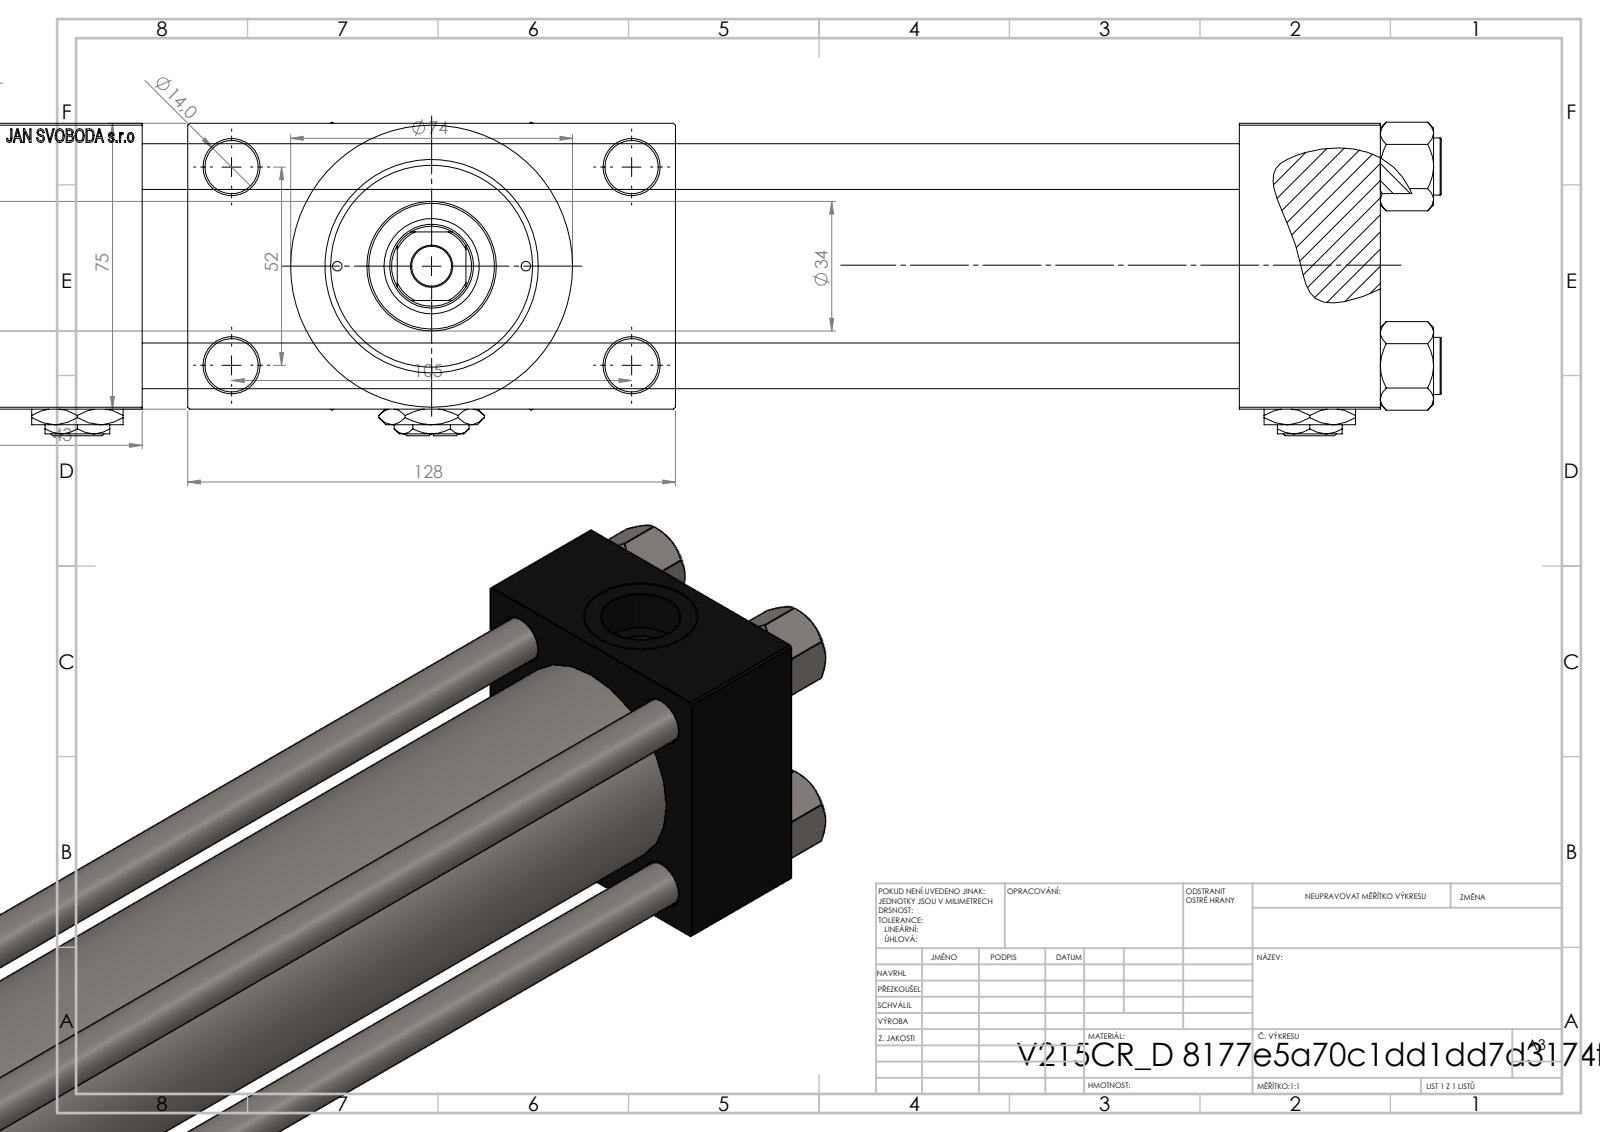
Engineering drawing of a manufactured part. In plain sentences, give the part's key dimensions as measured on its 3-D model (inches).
The part is named "V215CR_D_TYCINKA; V215CR_D_Body; V215CR_VCP_D; Zatka_pro_OIL_PORT (+2 more)". Its 3-D file was written by "SolidWorks 2019 (CONFIG_CONTROL_DESIGN)". It is 13 solids with 1213 faces: 547 planar, 104 cylindrical and 562 other. Overall it measures 16.732 by 5.039 by 3.239 inches. Its volume is 67.61 cubic inches and its surface area 459.3 square inches. Round holes: 4 of diameter 0.472, 4 of diameter 0.551, 2 of diameter 0.098, 2 of diameter 0.276, 2 of diameter 0.825, 2 of diameter 1.181, 1 of diameter 0.413, 1 of diameter 0.866, 1 of diameter 0.984, 1 of diameter 1.614, 1 of diameter 1.969, 1 of diameter 2.087. Round bosses or shafts: 4 of diameter 0.591, 1 of diameter 2.913, 1 of diameter 2.205, 1 of diameter 1.339. Partial cylindrical surfaces (rounded edges, fillets, slot ends): 1 of radius 0.413. The main face-to-face distances are 2.953, 11.339, 1.457, 12.795, 1.043, 3.996, 14.488, 13.031, 1.693, 0.63. The hole center spacings are 1.031, 1.037, 1.456, 1.497, 2.059, 2.253, 2.3, 2.307.
